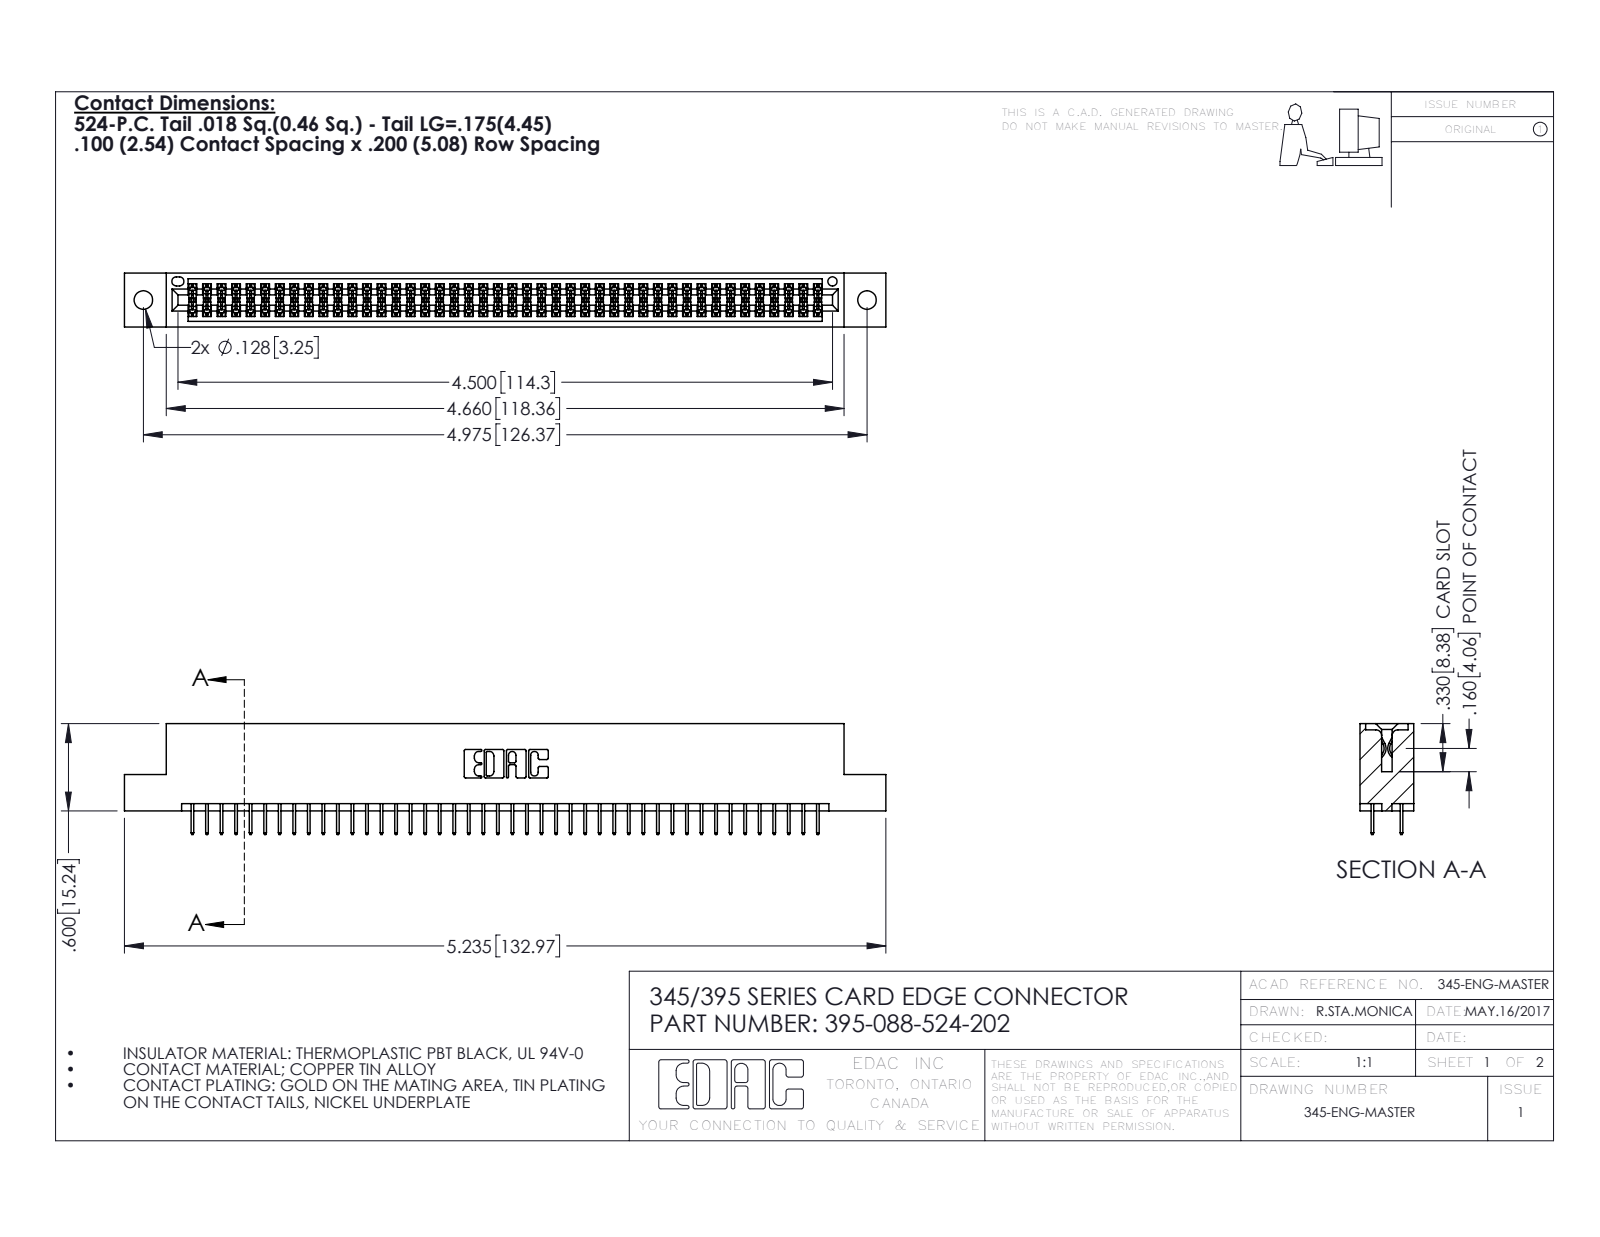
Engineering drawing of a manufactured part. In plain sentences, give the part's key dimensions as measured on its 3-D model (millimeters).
The part is named "345 Part_Flush Mounting Lugs - 0.128 Dia; 345-292-001_345-293-124; 395-088-524-202". Its 3-D file was written by "SolidWorks 2016 (CONFIG_CONTROL_DESIGN)". It is 89 solids with 4878 faces: 3512 planar, 1366 cylindrical and 0 other. Overall it measures 133 by 19.4 by 9.4 millimeters. Its volume is 12 800 cubic millimeters and its surface area 18 280 square millimeters. Round holes: 2 of diameter 3.3, 1 of diameter 1.6. Partial cylindrical surfaces (rounded edges, fillets, slot ends): 132 of radius 0.2, 22 of radius 0.3, 6 of radius 0.2, 6 of radius 0.8, 3 of radius 0.7, 2 of radius 0.4, 2 of radius 0.5, 2 of radius 0.6. The main face-to-face distances are 7.6, 1.8, 5.1, 9.4, 2.5, 6.9, 0.6, 5.7, 1.8, 4.4. The hole center spacings are 6.9, 120.4, 126.4.
